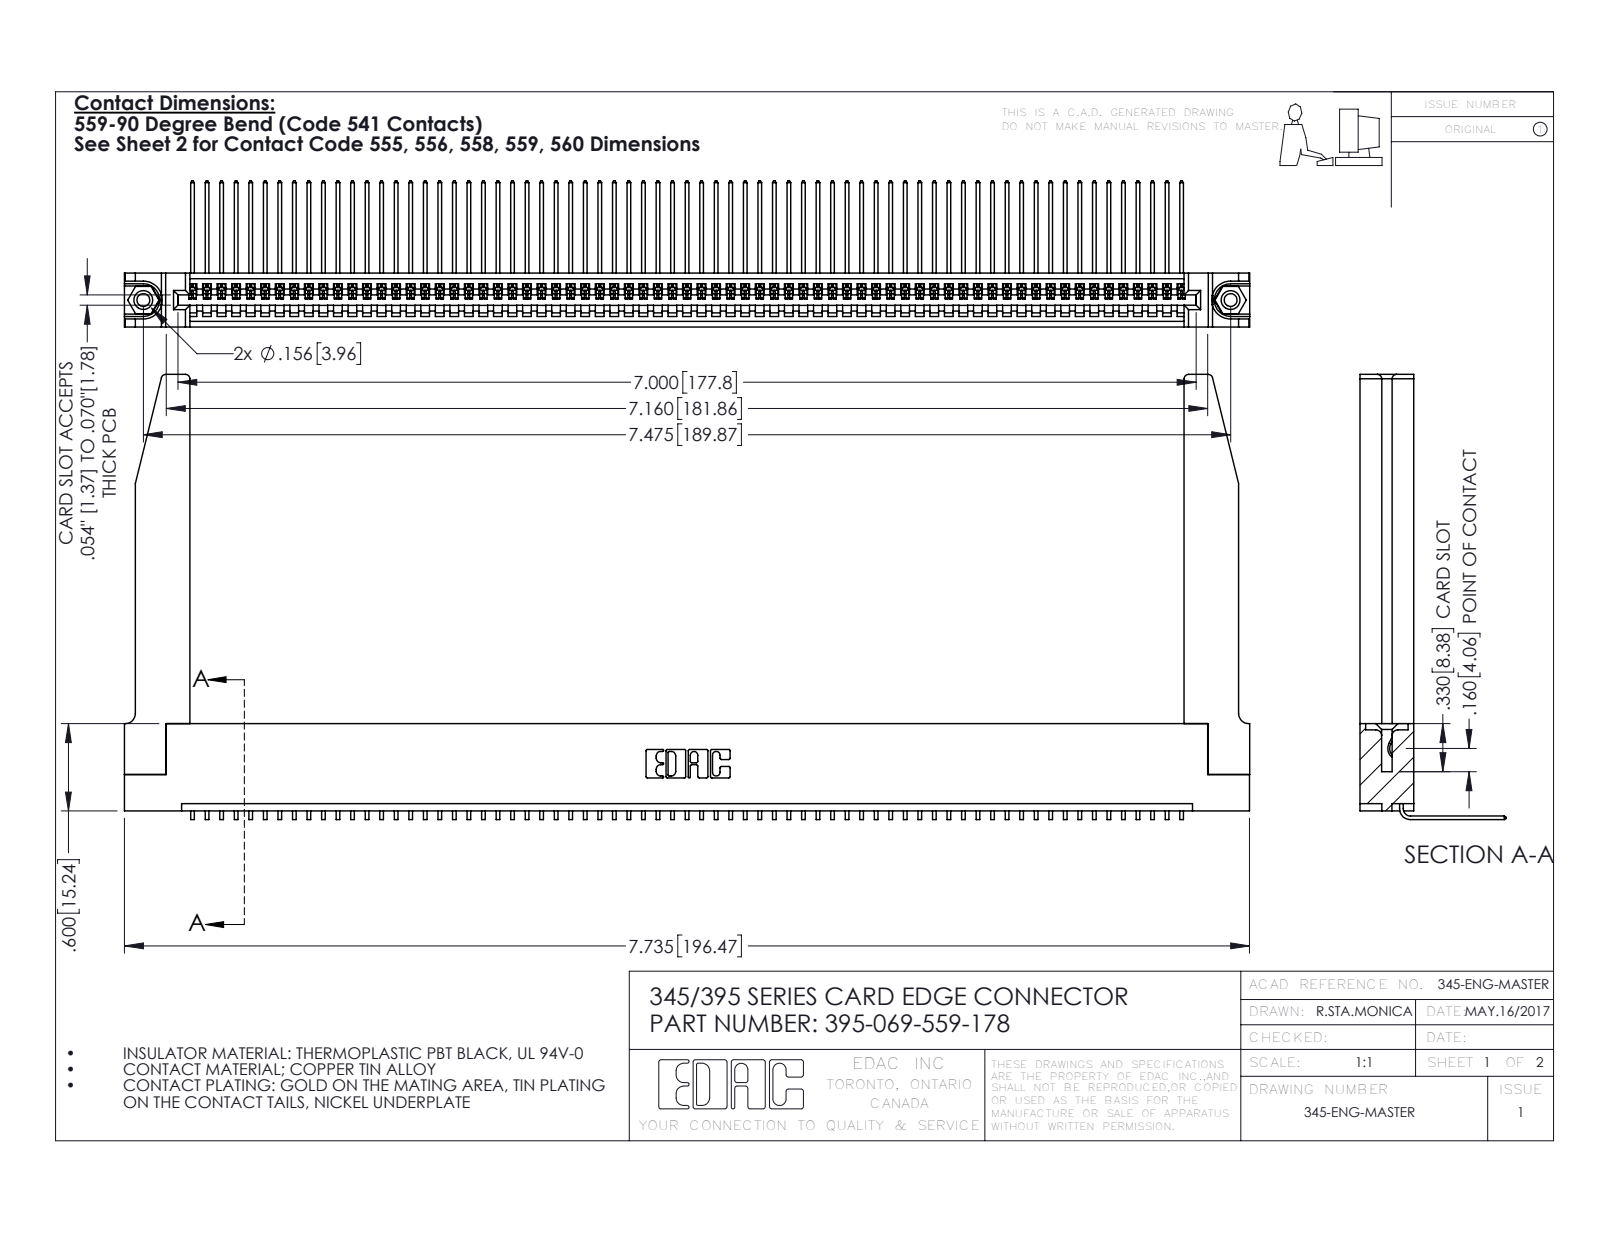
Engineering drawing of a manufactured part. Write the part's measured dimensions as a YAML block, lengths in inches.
part_name: "345 Part_Flush Mounting Lugs - 0.156 Dia-TH; 345-292-001_558 559 Tail - 1; 345-250-001_345-250-001-102; 345-220-078_345-220-078 (+1 more)"
step_written_by: "SolidWorks 2016 (CONFIG_CONTROL_DESIGN)"
units: inches
bodies: {solids: 74, faces: 4500, planar: 3120, cylindrical: 1328, other: 52}
overall_size: [7.736, 3.059, 1.005]
volume: 1.641
surface_area: 52.65
round_holes:
  - {diameter: 0.089, count: 2}
  - {diameter: 0.125, count: 2}
  - {diameter: 0.156, count: 2}
  - {diameter: 0.064, count: 1}
round_bosses_or_shafts:
  - {diameter: 0.155, count: 2}
partial_cylinders:
  - {radius: 0.006, count: 138}
  - {radius: 0.01, count: 22}
  - {radius: 0.03, count: 8}
  - {radius: 0.007, count: 6}
  - {radius: 0.031, count: 6}
  - {radius: 0.026, count: 3}
  - {radius: 0.031, count: 2}
  - {radius: 0.04, count: 2}
face_to_face_distances: [0.072, 0.37, 0.298, 0.2, 0.098, 0.272, 0.025, 0.225, 0.149, 0.148]
hole_center_spacings: [0.27, 7.239, 7.475]
